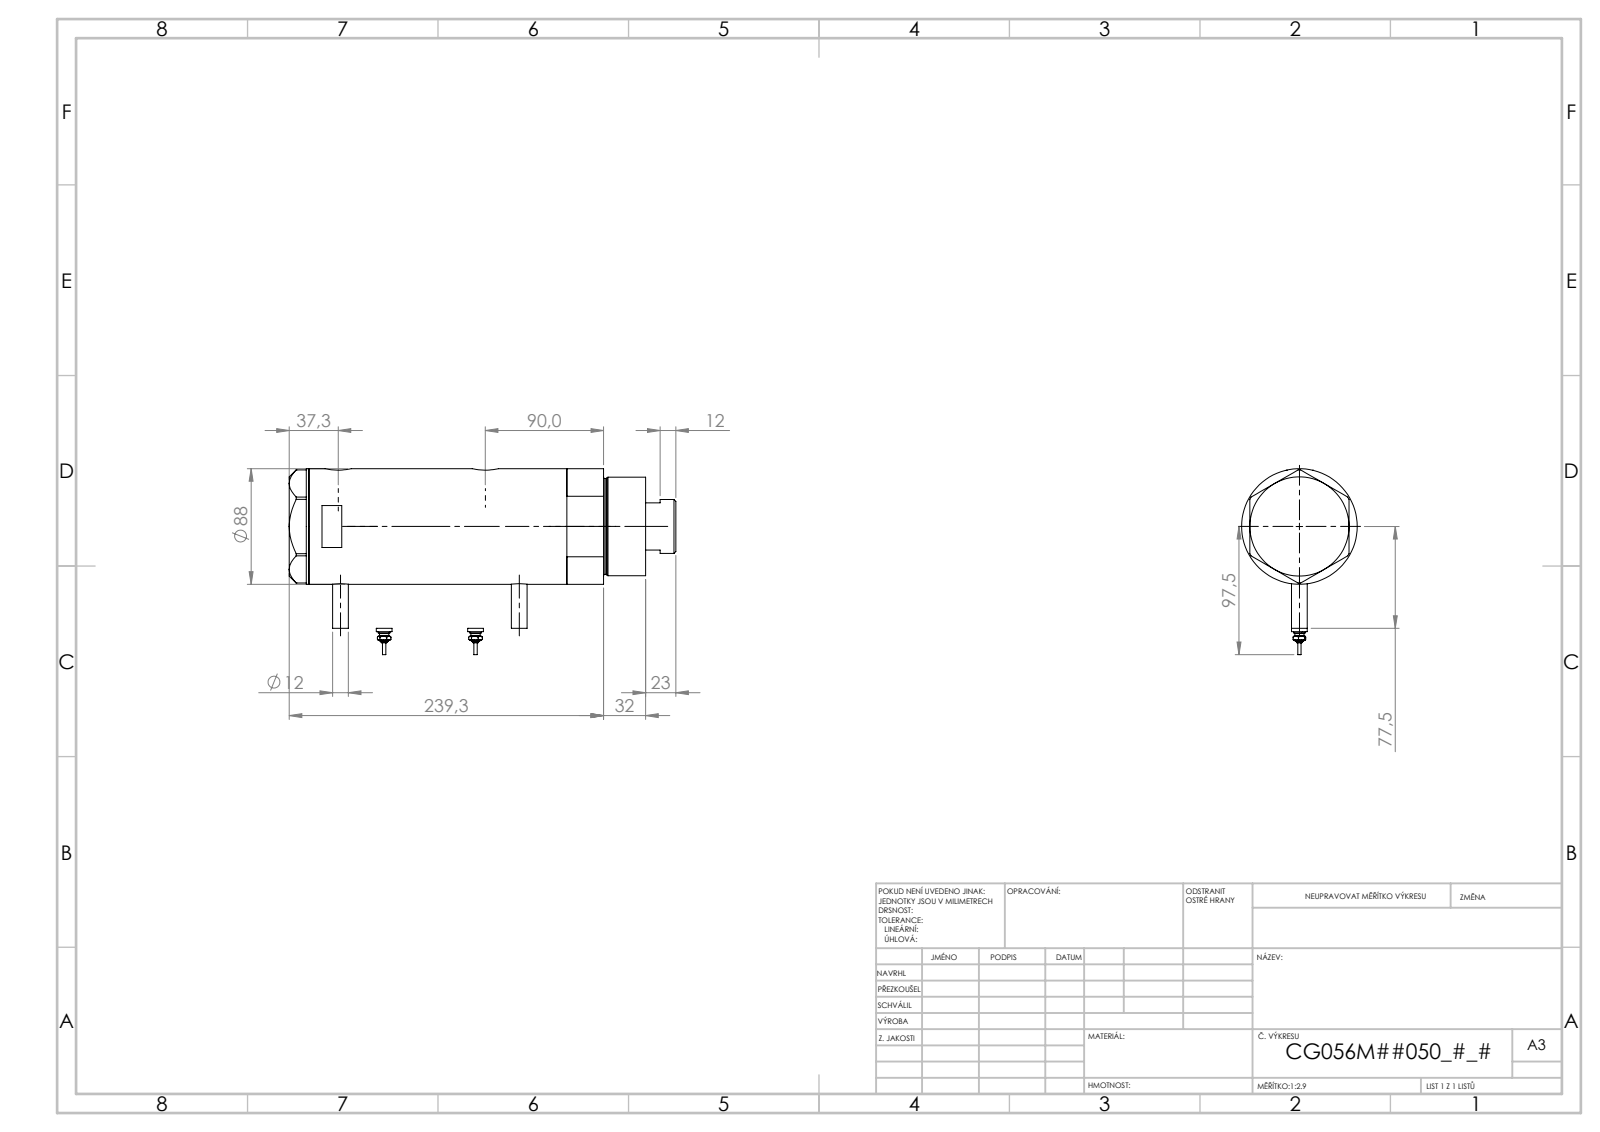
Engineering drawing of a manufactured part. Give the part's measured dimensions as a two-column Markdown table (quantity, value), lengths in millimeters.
| quantity | value |
| --- | --- |
| part name | V270CG_BACK; V270CG_FRONT; V270CG_SWITCH; V270CG_MIDDLE (+1 more) |
| STEP written by | SolidWorks 2019 (CONFIG_CONTROL_DESIGN) |
| units | millimeters |
| bodies | 6 solids, 232 faces (81 planar, 77 cylindrical, 74 other) |
| overall size | 274.47 × 120.3 × 88 |
| volume | 1 415 000 mm³ |
| surface area | 211 423 mm² |
| round holes (diameter × count) | 5 × 2, 12.5 × 2, 13.16 × 2, 20 × 2, 14.5 × 1, 42 × 1, 43.5 × 1, 56 × 1, 60 × 1, 80 × 1 |
| round bosses / shafts (diameter × count) | 12 × 2, 9 × 2, 7 × 2, 4.34 × 2, 2.4 × 2, 88 × 1, 75 × 1, 73 × 1 |
| main face-to-face distances | 124.4, 26, 98.4, 15, 41, 139.4, 236.47, 251.47, 210.47, 112.07 |
| hole center spacings | 1.7, 25.8, 100.3, 102, 126.1, 127.8 |
